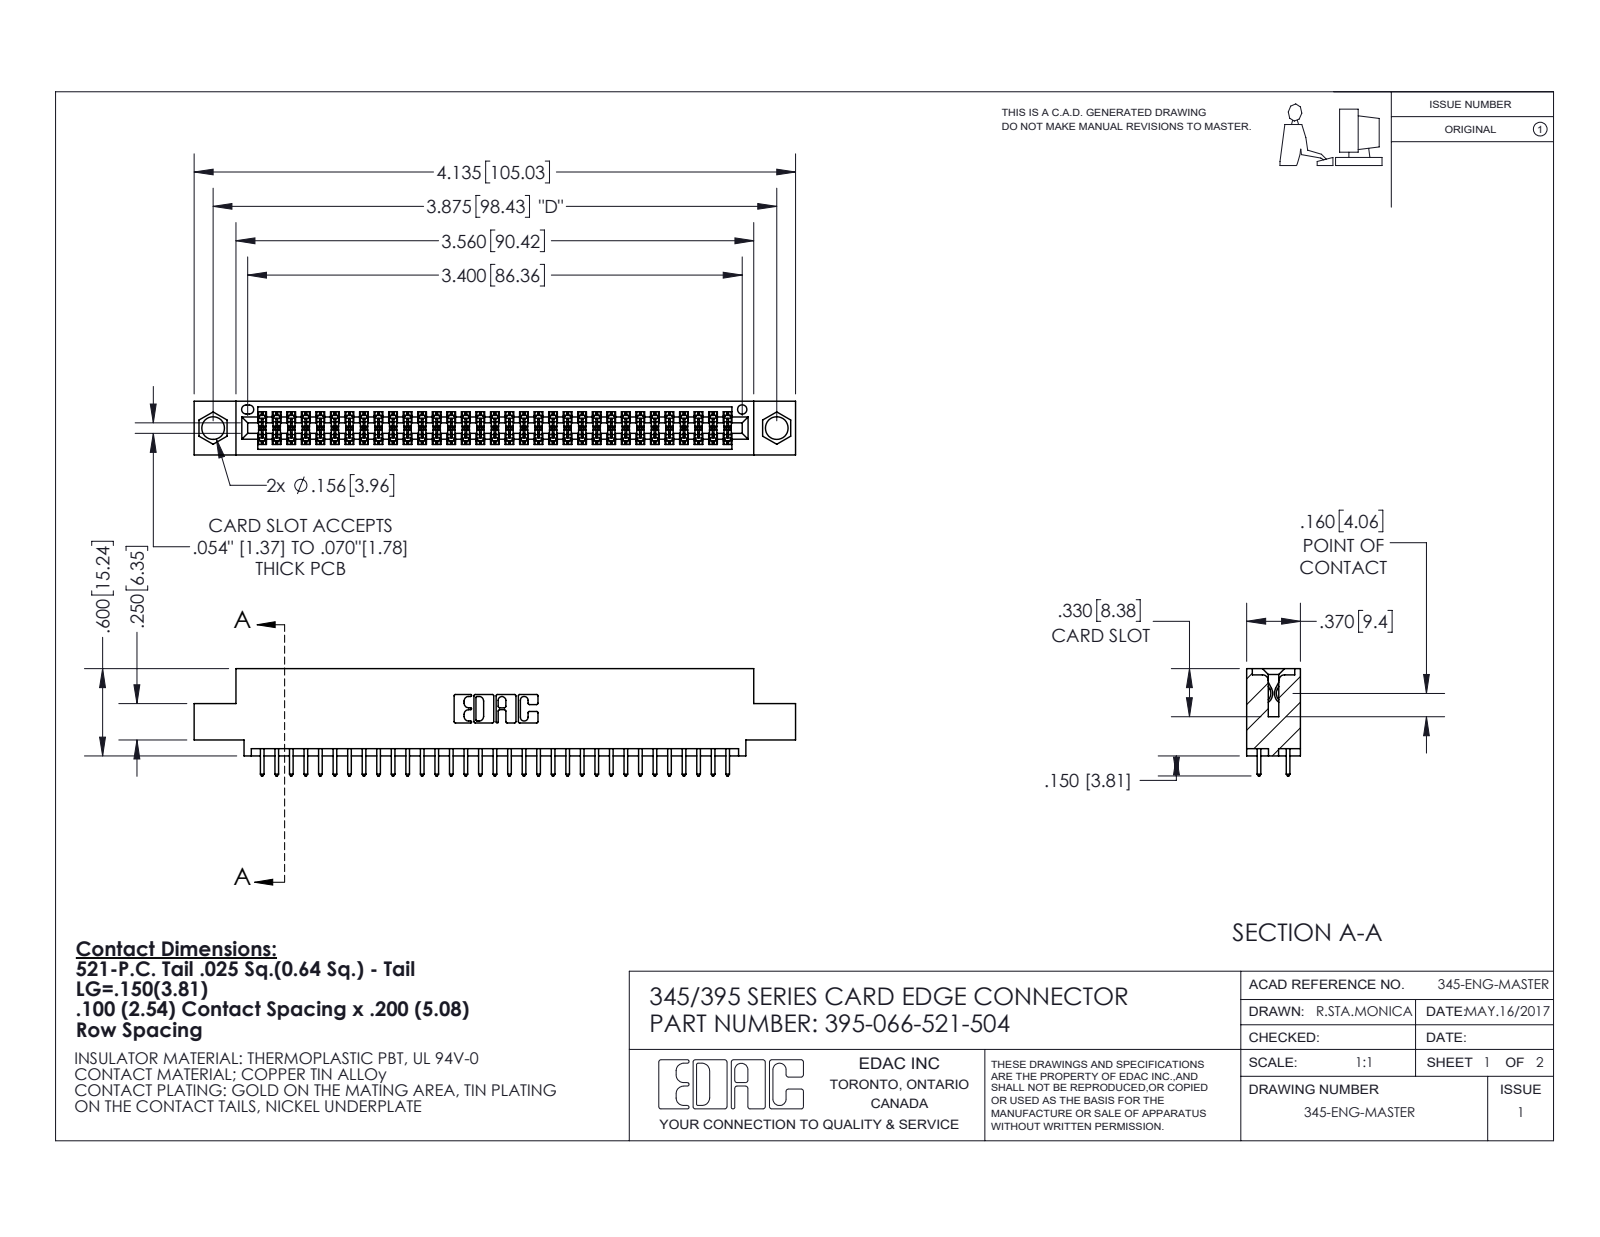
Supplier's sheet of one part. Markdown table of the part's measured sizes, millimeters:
| quantity | value |
| --- | --- |
| part name | 345-292-001_345-293-121; 395-066-521-504; 345 Part_0.110 Offset - 0.156 Dia-TI |
| STEP written by | SolidWorks 2020 (CONFIG_CONTROL_DESIGN) |
| units | millimeters |
| bodies | 67 solids, 3444 faces (2276 planar, 1168 cylindrical, 0 other) |
| overall size | 105 × 18.7 × 9.4 |
| volume | 9 910 mm³ |
| surface area | 14 250 mm² |
| round holes (diameter × count) | 4 × 2, 1.6 × 1 |
| partial cylindrical surfaces (radius × count) | 0.2 × 132, 0.3 × 66, 0.3 × 22, 0.2 × 6, 0.8 × 6, 0.7 × 3, 0.4 × 2, 0.5 × 2 |
| main face-to-face distances | 1.8, 7.6, 5.1, 9.4, 2.5, 6.9, 0.6, 5.7, 4.4, 3.8 |
| hole center spacings | 6.9, 92.5, 98.4 |
